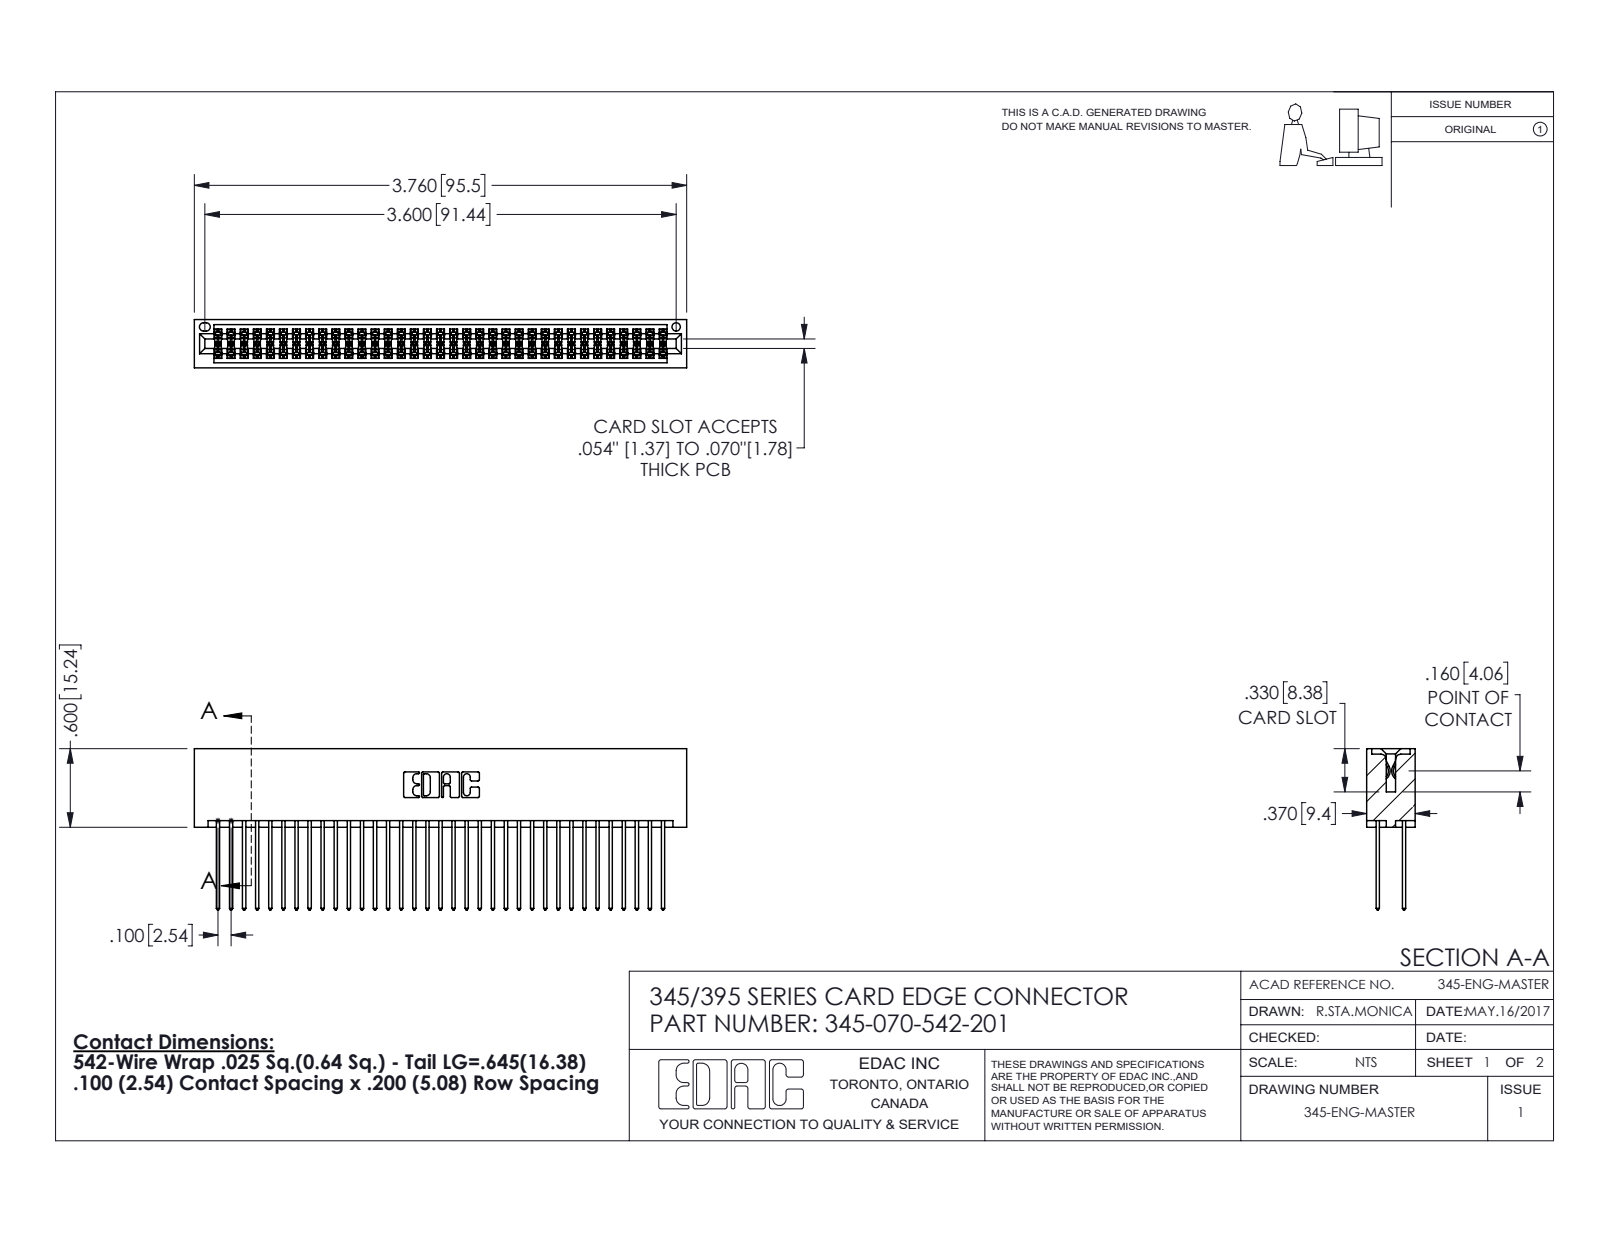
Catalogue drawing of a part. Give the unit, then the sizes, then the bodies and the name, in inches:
Units: inches
Overall size (bounding box): 3.76 × 1.232 × 0.37
Round holes (diameter × count): ⌀0.064 ×1
Partial cylindrical surfaces — rounded edges, fillets, slot ends (radius × count): R0.006 ×105, R0.01 ×70, R0.01 ×22, R0.007 ×6, R0.031 ×6, R0.026 ×3, R0.014 ×2, R0.019 ×2
Main face-to-face distances: 0.298, 0.072, 0.2, 0.098, 0.272, 0.025, 0.225, 0.37, 0.175, 0.149
Volume: 0.62 in³ · Surface area: 25.89 in²
Bodies: 71 solids, 3618 faces (2386 planar, 1232 cylindrical, 0 other)
Part name (STEP PRODUCT): 345-292-001_345-293-142; 345 Part_No Mounting Lugs; 345-070-542-201
STEP written by: SolidWorks 2016 (CONFIG_CONTROL_DESIGN)
